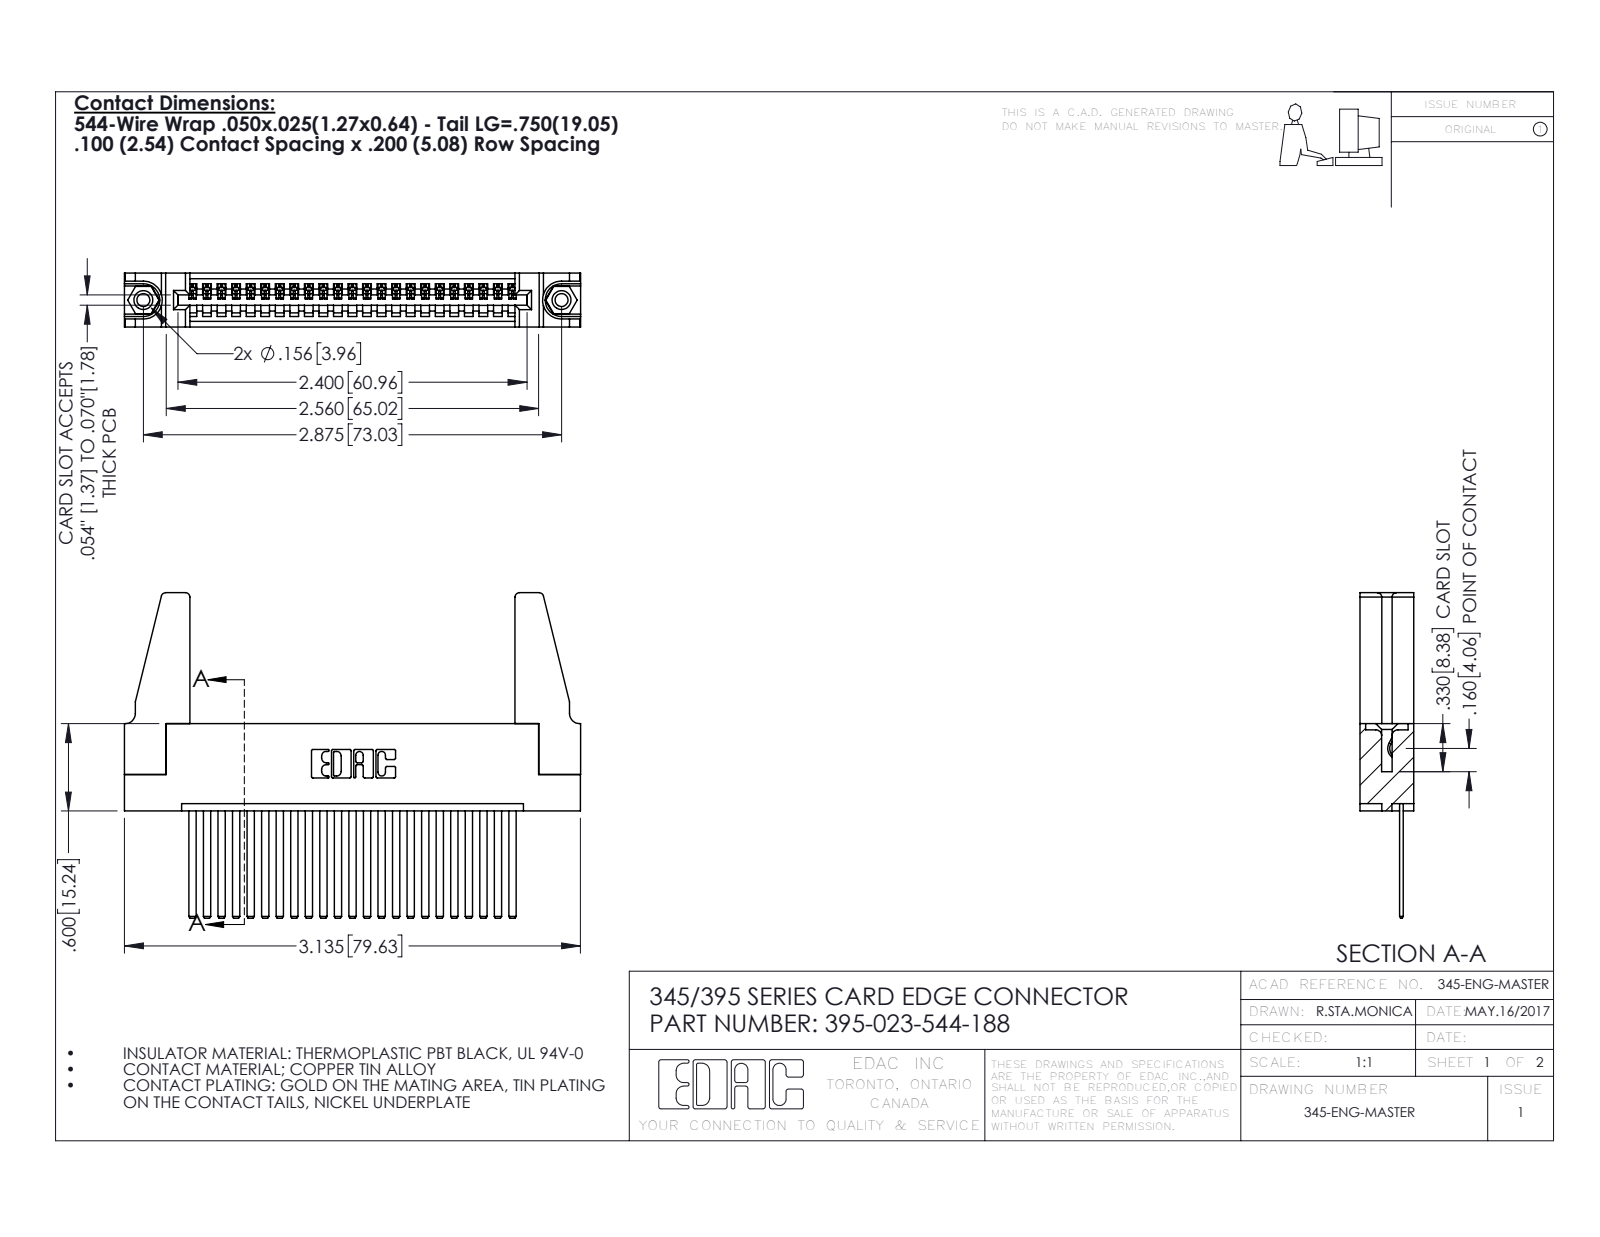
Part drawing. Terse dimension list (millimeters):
name: 395-023-544-188; 345-250-001_345-250-001-102; 345 Part_Flush Mounting Lugs - 0.156 Dia-TH; 345-220-078_345-220-088 (+1 more)
written by: SolidWorks 2016 (CONFIG_CONTROL_DESIGN)
unit: mm
bodies: 28 solids, 1446 faces (980 planar, 450 cylindrical, 16 other)
size: 79.7 × 56.8 × 9.4
volume: 10 900 mm³; area: 13 870 mm²
holes: 2× ⌀2.3, 2× ⌀3.2, 2× ⌀4, 1× ⌀1.6
bosses: 2× ⌀3.9
rounds: 46× R0.2, 22× R0.3, 8× R0.8, 6× R0.2, 6× R0.8, 3× R0.7, 2× R0.8, 2× R1
face distances: 1.8, 7.6, 9.4, 2.5, 6.9, 0.6, 5.1, 5.7, 3.8, 3.8
hole spacings: 6.9, 67.1, 73
